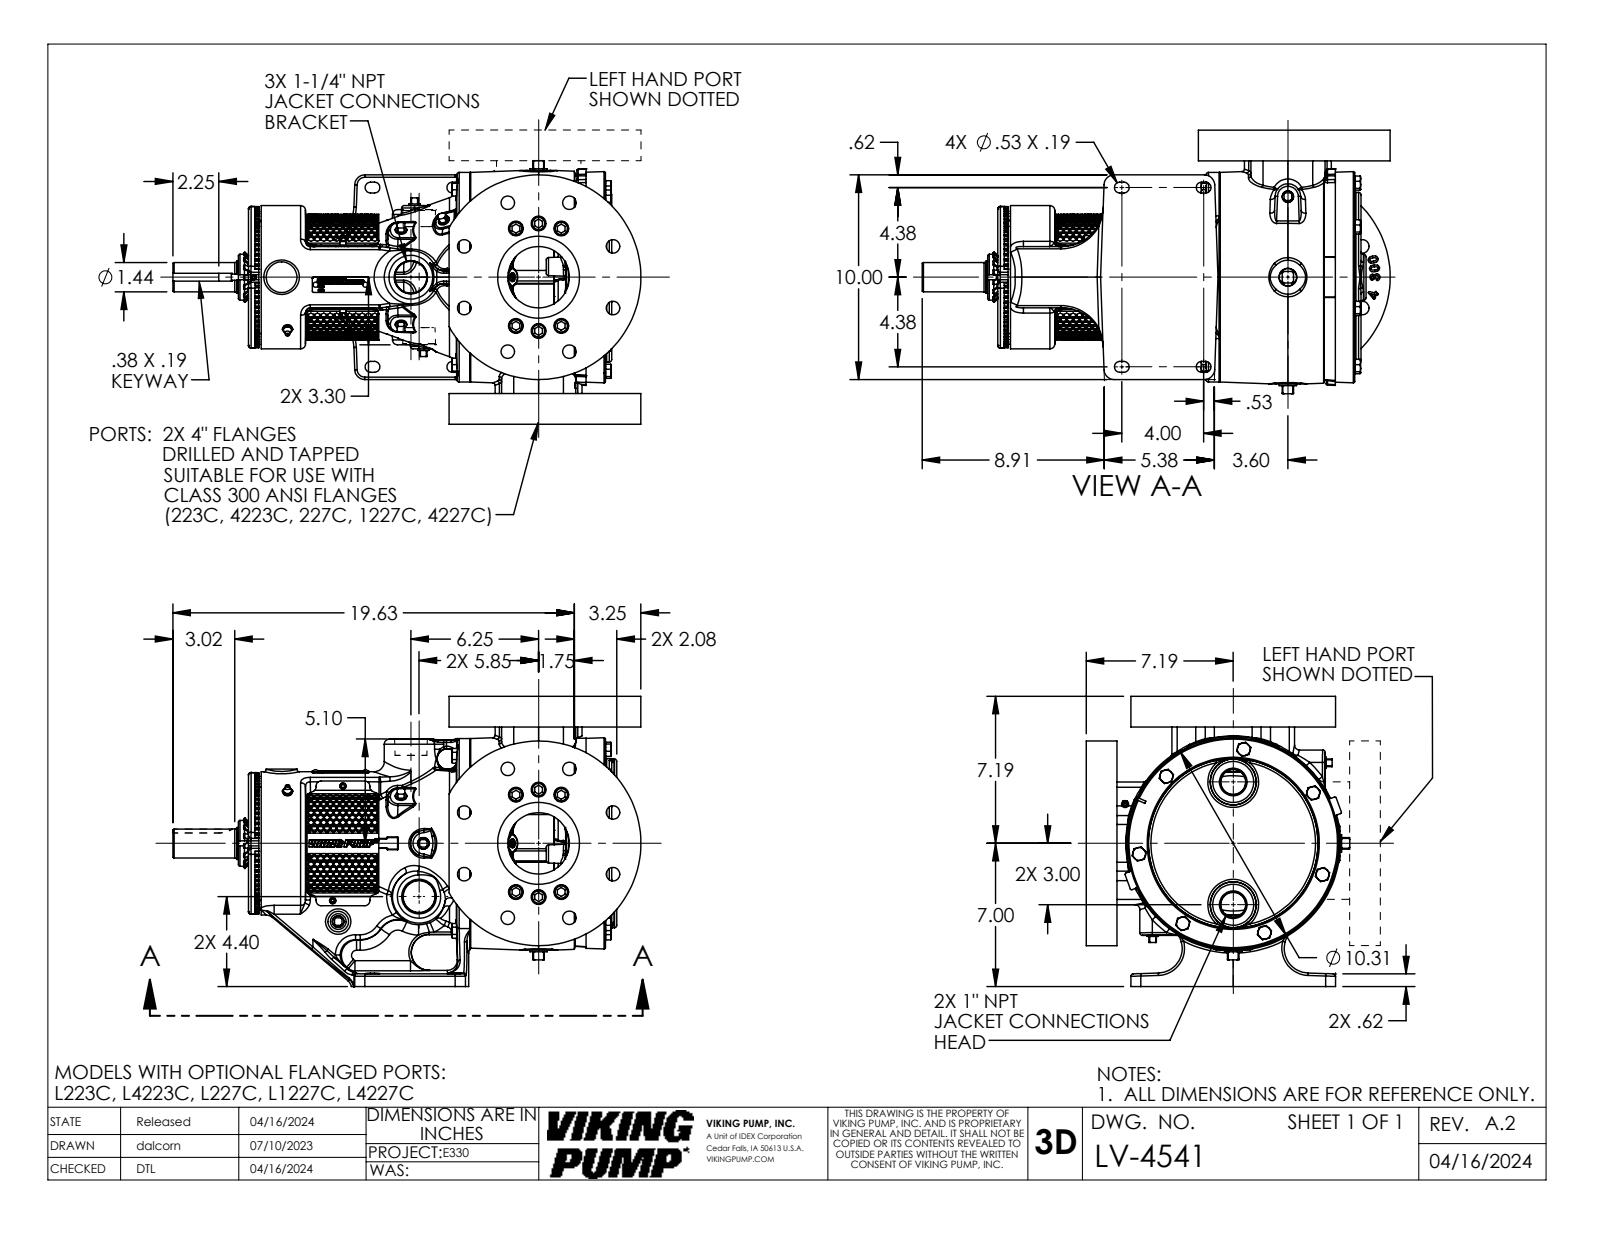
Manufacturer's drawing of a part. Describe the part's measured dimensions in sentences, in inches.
The part is named "LV-4541". Its 3-D file was written by "SolidWorks 2022 (AUTOMOTIVE_DESIGN)". It is 1 solid with 4461 faces: 1514 planar, 897 cylindrical and 2050 other. Overall it measures 22.881 by 14.188 by 12.878 inches. Its volume is 1 211 cubic inches and its surface area 1 590 square inches. Round holes: 16 of diameter 0.656, 12 of diameter 0.469, 12 of diameter 0.719, 8 of diameter 1.094, 6 of diameter 0.199, 6 of diameter 0.25, 3 of diameter 0.159, 2 of diameter 0.266, 2 of diameter 0.313, 2 of diameter 3, 1 of diameter 0.453, 1 of diameter 1.577. Round bosses or shafts: 15 of diameter 0.437, 12 of diameter 0.66, 9 of diameter 0.625, 6 of diameter 0.625, 3 of diameter 0.312, 2 of diameter 10, 1 of diameter 10.25, 1 of diameter 7. Partial cylindrical surfaces (rounded edges, fillets, slot ends): 109 of radius 0.063, 74 of radius 0.069, 58 of radius 0.12, 26 of radius 0.5, 18 of radius 0.03, 16 of radius 0.24, 16 of radius 1, 13 of radius 0.06. The main face-to-face distances are 1.5, 12.687, 14.187, 0.31, 2.25, 14.696, 15.006, 11.46, 2.75, 0.5. The hole center spacings are 7.276, 3, 3.937, 2.625, 1.375, 1.136, 2.18, 2.675.
